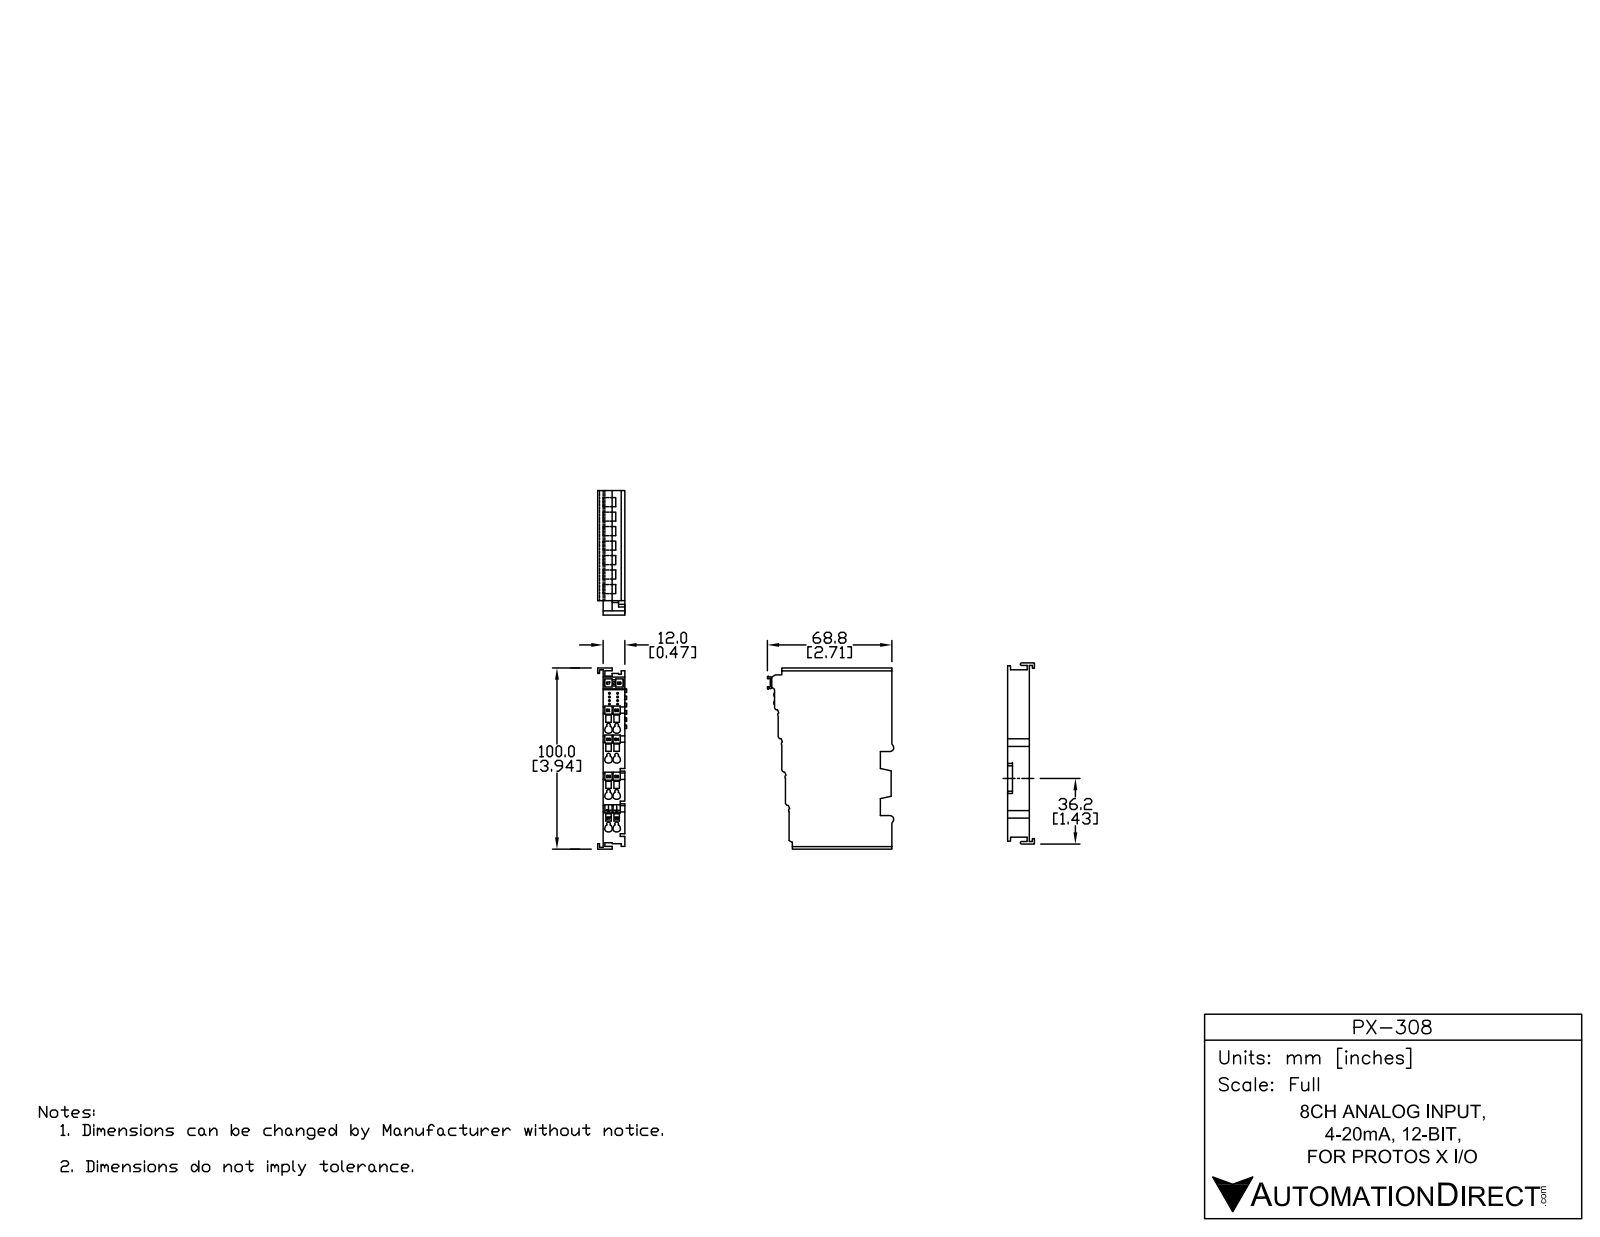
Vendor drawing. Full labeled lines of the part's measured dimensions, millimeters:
Part name (STEP PRODUCT): PX-308
STEP written by: SolidWorks 2014 (AUTOMOTIVE_DESIGN)
Units: millimetres
Bodies: 26 solids, 1425 faces (1011 planar, 354 cylindrical, 60 other)
Overall size (bounding box): 100.25 × 69.28 × 15.15
Volume: 59 090 mm³ · Surface area: 32 341 mm²
Round holes (diameter × count): ⌀4 ×8
Partial cylindrical surfaces — rounded edges, fillets, slot ends (radius × count): R0.25 ×67, R0.3 ×43, R0.38 ×12, R0.4 ×10, R1 ×8, R0.17 ×4, R1.03 ×4, R1.38 ×4
Main face-to-face distances: 12, 2, 10, 1, 1.85, 11, 4, 8.7, 3.15, 1.22
Hole centre spacings: 5, 18.4, 19.07, 16, 16.76, 34.4, 34.76, 36.8
